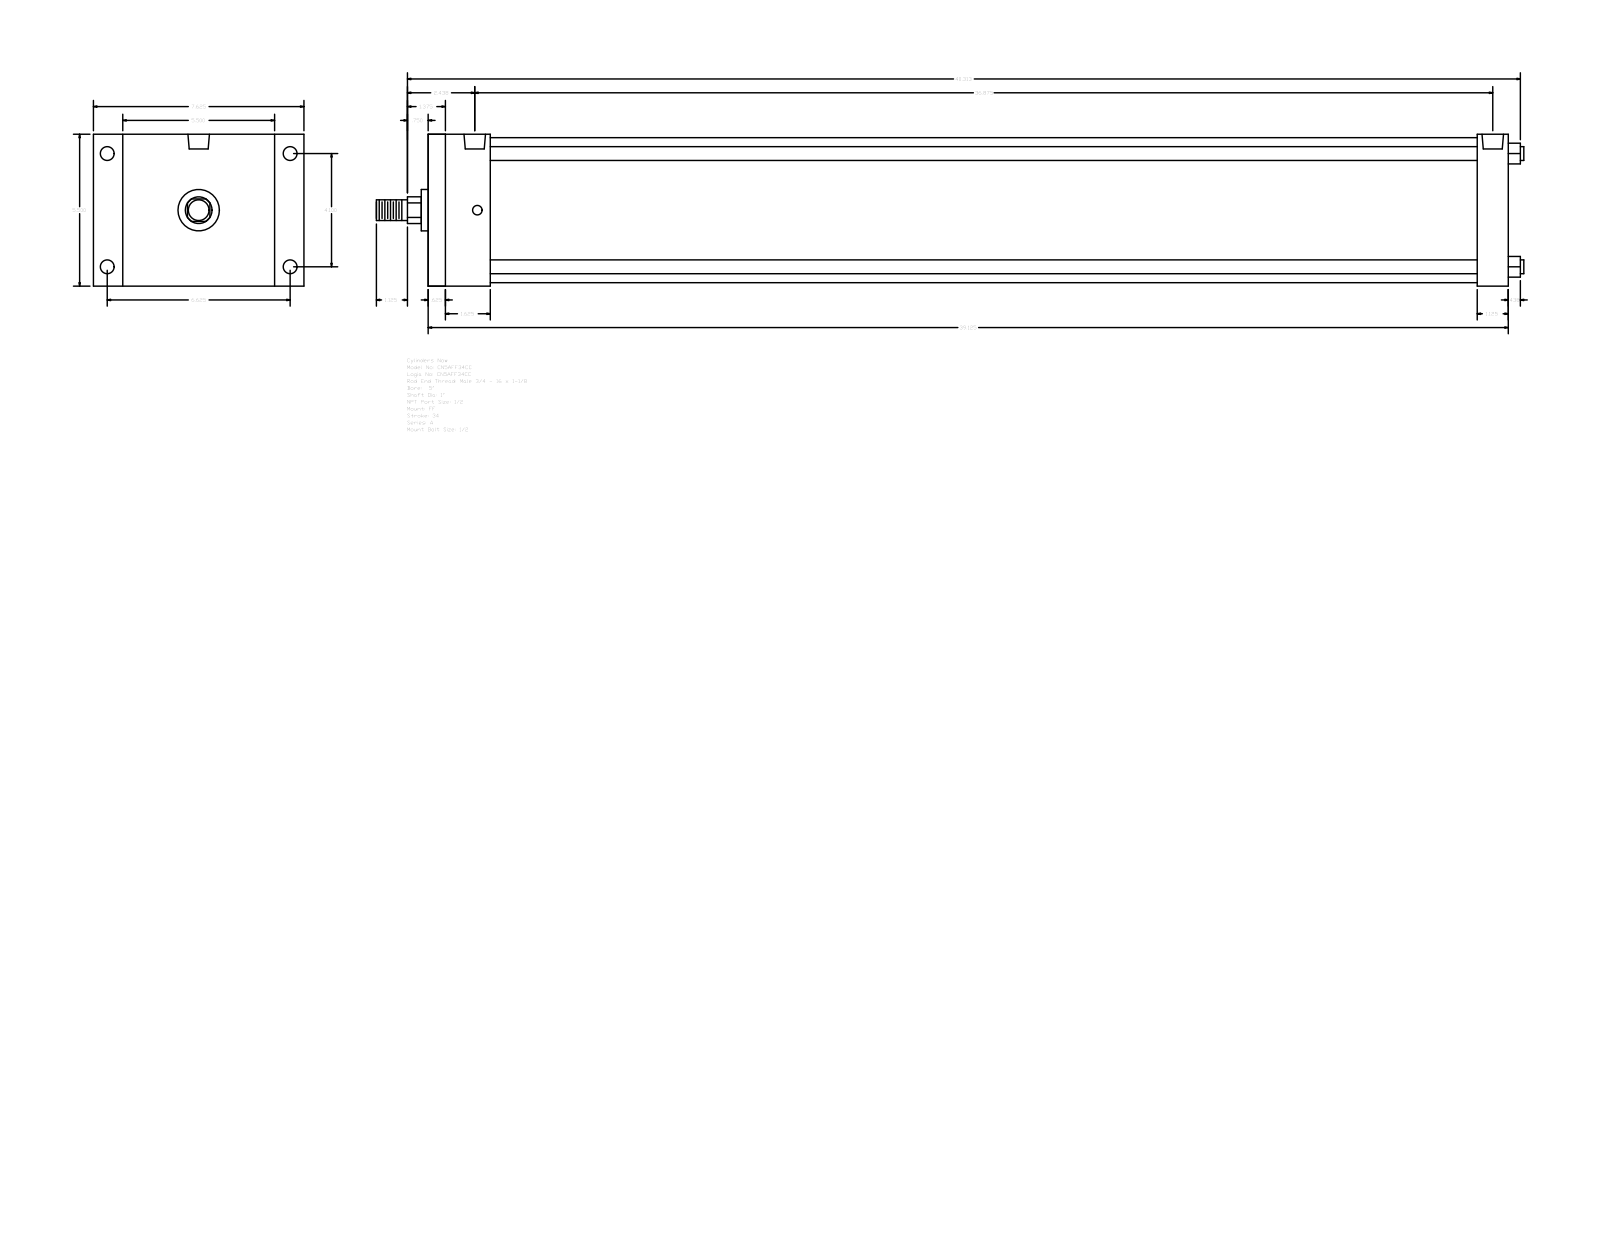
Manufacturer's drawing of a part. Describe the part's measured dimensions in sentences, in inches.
The part is named "A_FF__0500_1". Its 3-D file was written by "GSSL Pune (CONFIG_CONTROL_DESIGN)". It is 0 solids with 92 faces: 64 planar, 28 cylindrical and 0 other. Overall it measures 41.563 by 7.625 by 5.5 inches. Round holes: 4 of diameter 0.344, 4 of diameter 0.5, 2 of diameter 0.778. Round bosses or shafts: 4 of diameter 0.5, 1 of diameter 5.25, 1 of diameter 1.5, 1 of diameter 1, 1 of diameter 0.75. Partial cylindrical surfaces (rounded edges, fillets, slot ends): 1 of radius 0.484. The main face-to-face distances are 5.5, 39.125, 0.625, 38.5, 38, 37.375, 1.125, 2.25, 1.625, 35.75. The hole center spacings are 0.094, 4.1, 6.625, 7.791, 36.687, 36.781, 36.875.
